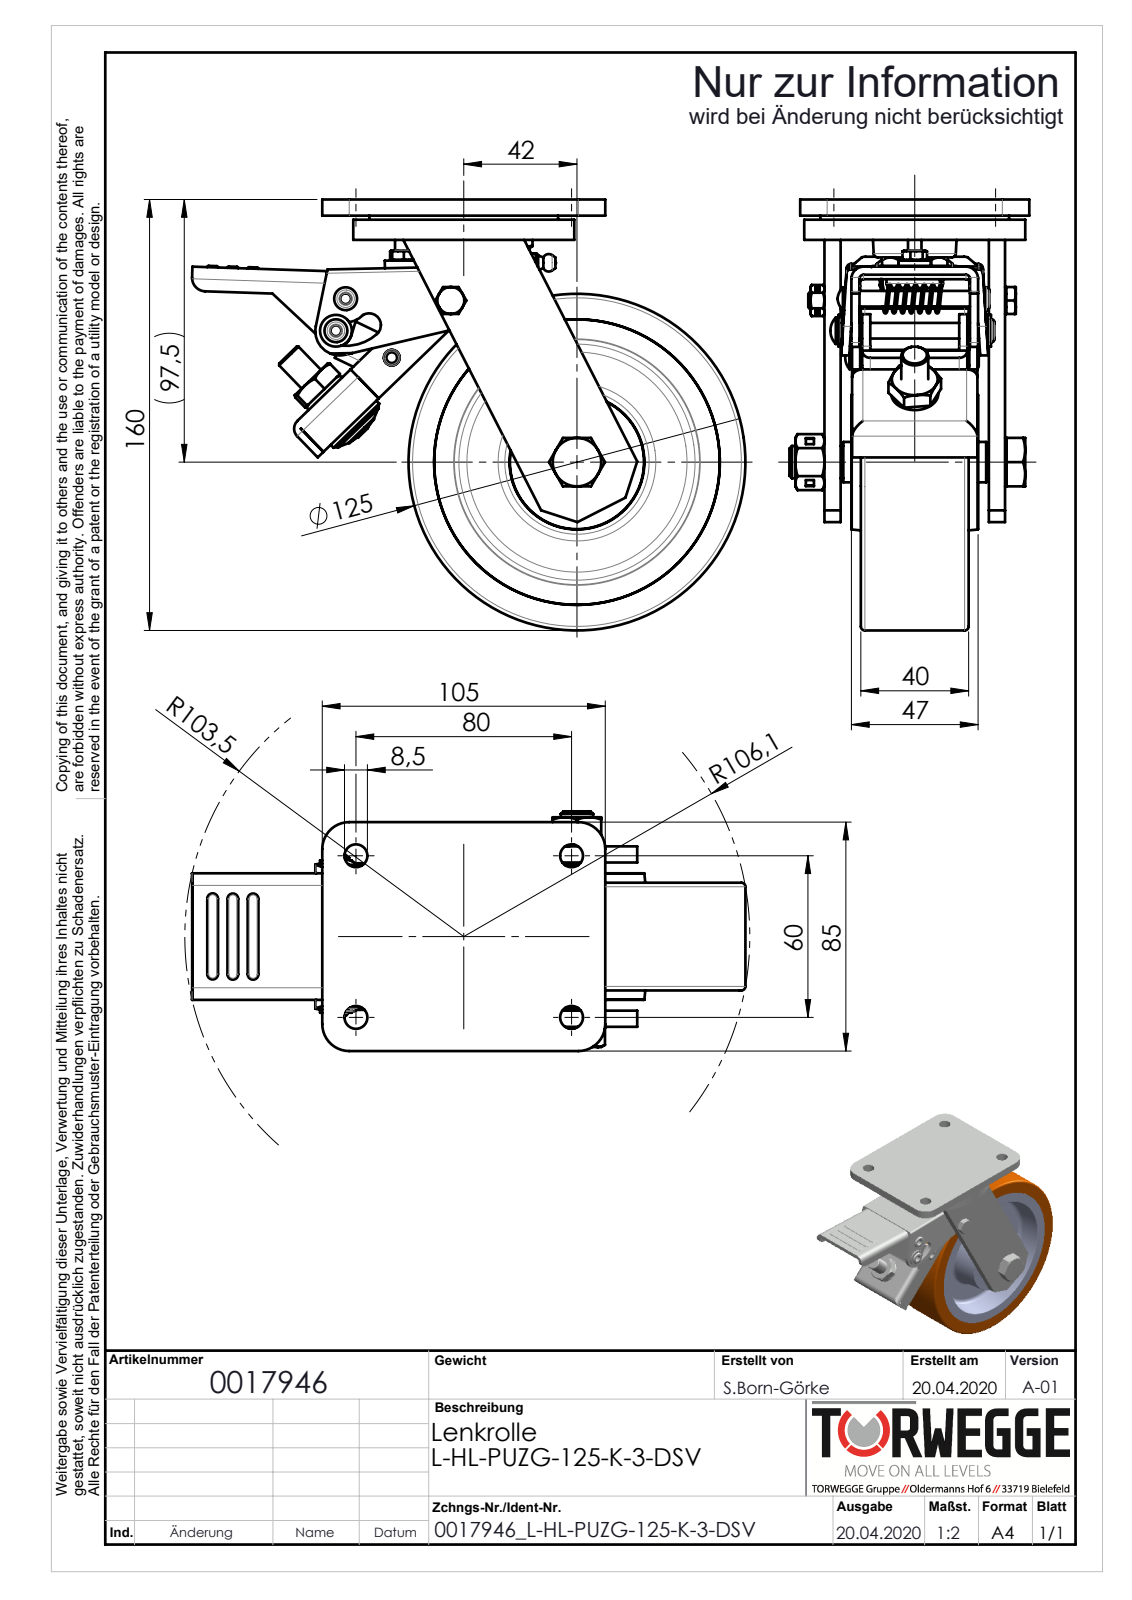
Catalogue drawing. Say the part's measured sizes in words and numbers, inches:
The part is named "0017946". Its 3-D file was written by "SolidWorks 2018 (AUTOMOTIVE_DESIGN)". It is 0 solids with 795 faces: 282 planar, 242 cylindrical and 271 other. Overall it measures 8.083 by 6.299 by 3.504 inches. Round holes: 4 of diameter 0.236, 4 of diameter 0.335, 3 of diameter 0.197, 2 of diameter 0.472, 2 of diameter 0.63, 1 of diameter 0.157, 1 of diameter 0.228, 1 of diameter 0.244, 1 of diameter 0.248, 1 of diameter 0.315, 1 of diameter 0.33, 1 of diameter 0.402. Round bosses or shafts: 2 of diameter 0.827, 2 of diameter 0.394, 2 of diameter 0.039, 1 of diameter 4.921, 1 of diameter 3.228, 1 of diameter 2.756, 1 of diameter 0.929, 1 of diameter 0.787. Partial cylindrical surfaces (rounded edges, fillets, slot ends): 16 of radius 0.059, 6 of radius 0.02, 4 of radius 0.039, 4 of radius 0.394, 3 of radius 0.157, 2 of radius 0.118, 2 of radius 0.173, 2 of radius 0.177. The main face-to-face distances are 0.236, 0.295, 0.531, 2.106, 2.402, 1.87, 0.118, 1.575, 0.591, 0.354. The hole center spacings are 1.969, 0.906, 1.357, 1.398, 2.362, 2.676, 2.747, 3.15.
